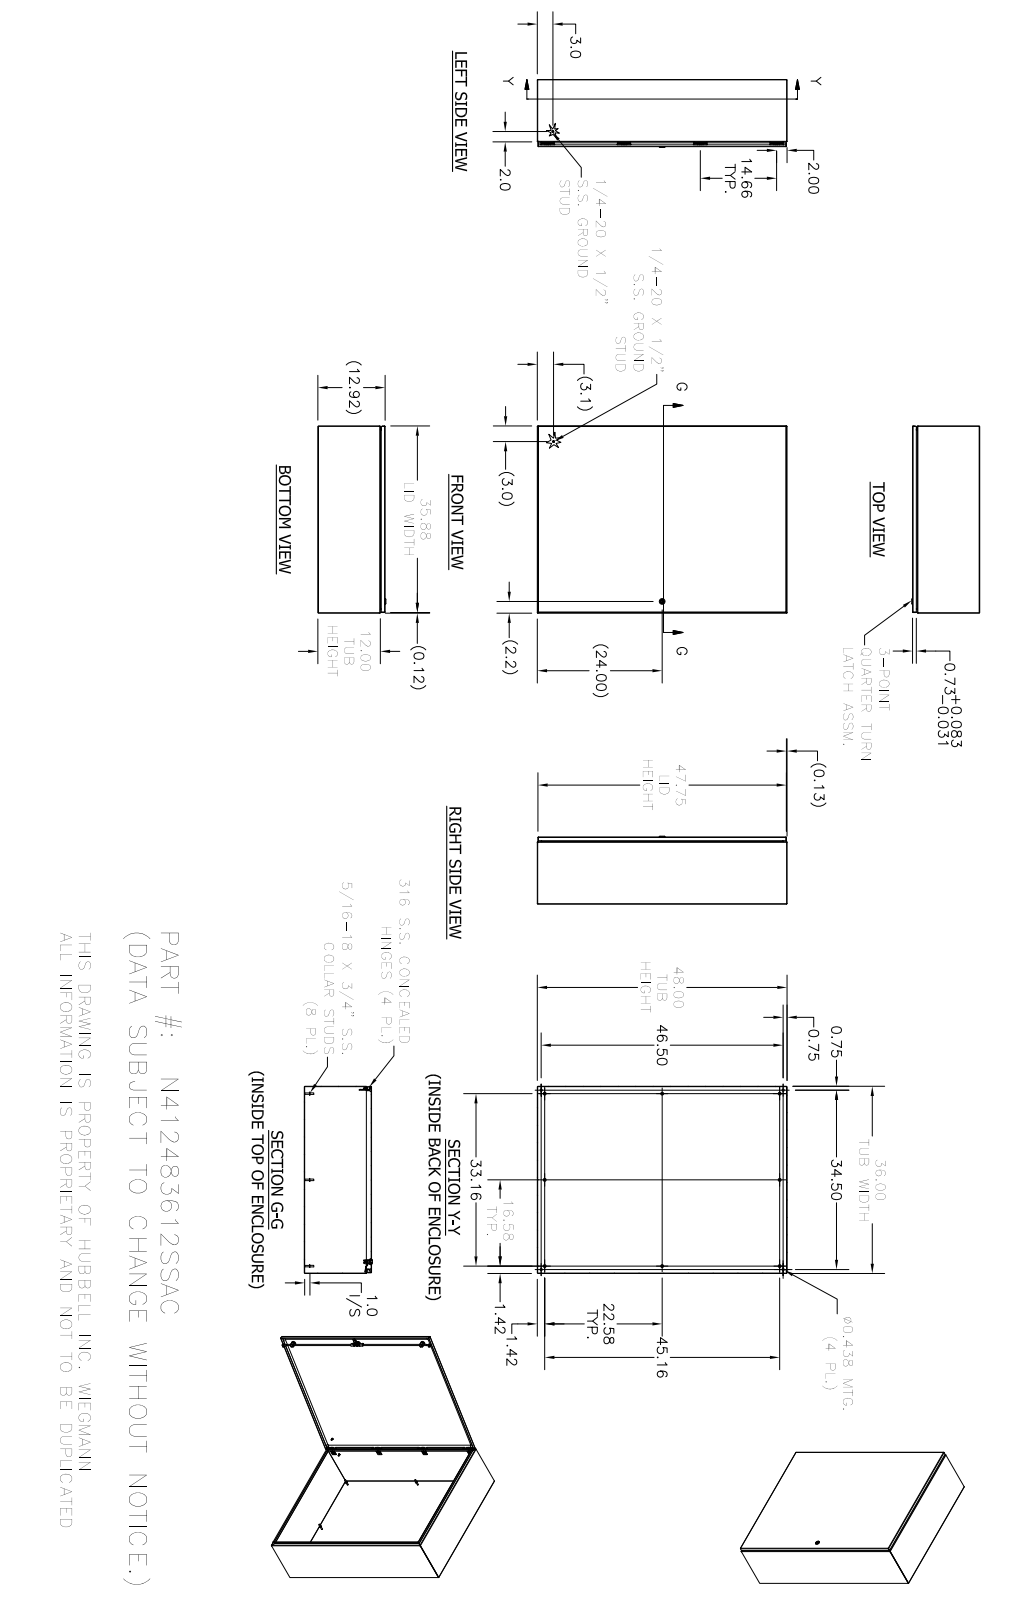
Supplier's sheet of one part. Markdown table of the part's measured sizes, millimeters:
| quantity | value |
| --- | --- |
| part name | N412483612SSACBTB; N4124812SSACLS; N4124812SSACRS; 388151 (+8 more) |
| STEP written by | Autodesk Inventor 2016 (AUTOMOTIVE_DESIGN) |
| units | millimeters |
| bodies | 82 solids, 2666 faces (979 planar, 994 cylindrical, 693 other) |
| overall size | 1219.2 × 914.4 × 332.1 |
| volume | 7 581 000 mm³ |
| surface area | 7 748 000 mm² |
| round holes (diameter × count) | 2.36 × 8, 3.86 × 8, 4.25 × 8, 4.37 × 8, 4.76 × 8, 5 × 5, 3.96 × 4, 4.2 × 4, 11.11 × 4, 2.7 × 2, 4.06 × 2, 4.3 × 2 |
| round bosses / shafts (diameter × count) | 6.35 × 18, 14.3 × 8, 9.14 × 8, 8.13 × 8, 7.62 × 8, 6.99 × 8, 6.5 × 8, 4.17 × 8 |
| partial cylindrical surfaces (radius × count) | 1.27 × 50, 0.79 × 36, 0.4 × 34, 3.17 × 32, 0.3 × 31, 0.5 × 20, 2.67 × 18, 0.81 × 16 |
| main face-to-face distances | 1.88, 326.22, 324.34, 328.1, 912.52, 1217.32, 910.64, 914.4, 1215.44, 1219.2 |
| hole center spacings | 372.53, 745.07, 372.54, 1117.6, 745.06, 12.7, 16.66, 372.75 |
